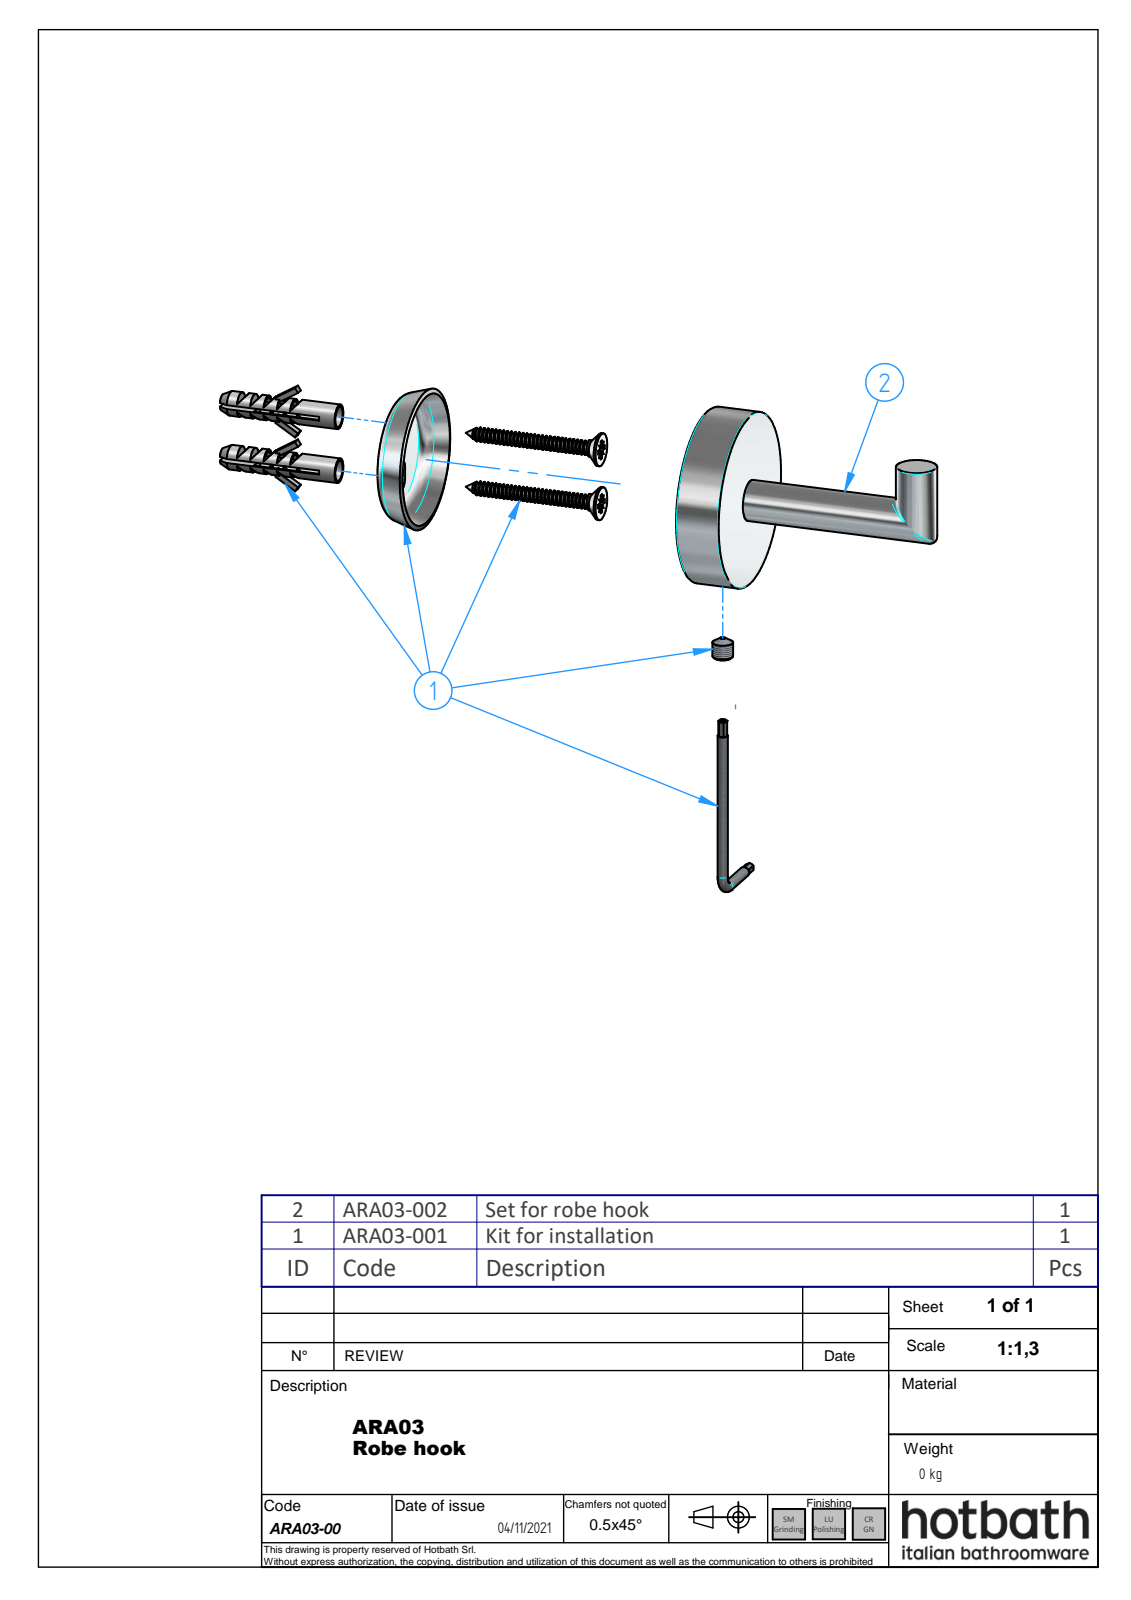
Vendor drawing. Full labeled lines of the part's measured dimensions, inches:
Part name (STEP PRODUCT): ARA03-00; ARA03-002_oa_0; ARA03-01; ARA03-02 (+3 more)
STEP written by: ST-DEVELOPER v16.7 (AP242_MANAGED_MODEL_BASED_3D_ENGINEERING_MIM_LF)
Units: inches
Bodies: 5 solids, 147 faces (112 planar, 18 cylindrical, 17 other)
Overall size (bounding box): 3.504 × 1.693 × 1.693
Volume: 0.596 in³ · Surface area: 15.42 in²
Round holes (diameter × count): ⌀0.163 ×2, ⌀0.197 ×2, ⌀1.551 ×1
Round bosses / shafts (diameter × count): ⌀0.394 ×2, ⌀0.236 ×2, ⌀1.693 ×1, ⌀0.197 ×1
Partial cylindrical surfaces — rounded edges, fillets, slot ends (radius × count): R0.171 ×1, R0.177 ×1, R0.701 ×1
Main face-to-face distances: 0.055, 0.433, 0.378, 0.039, 0.543, 0.098, 0.583, 0.793, 0.211, 0.504
Hole centre spacings: 0.222, 0.321, 0.543
